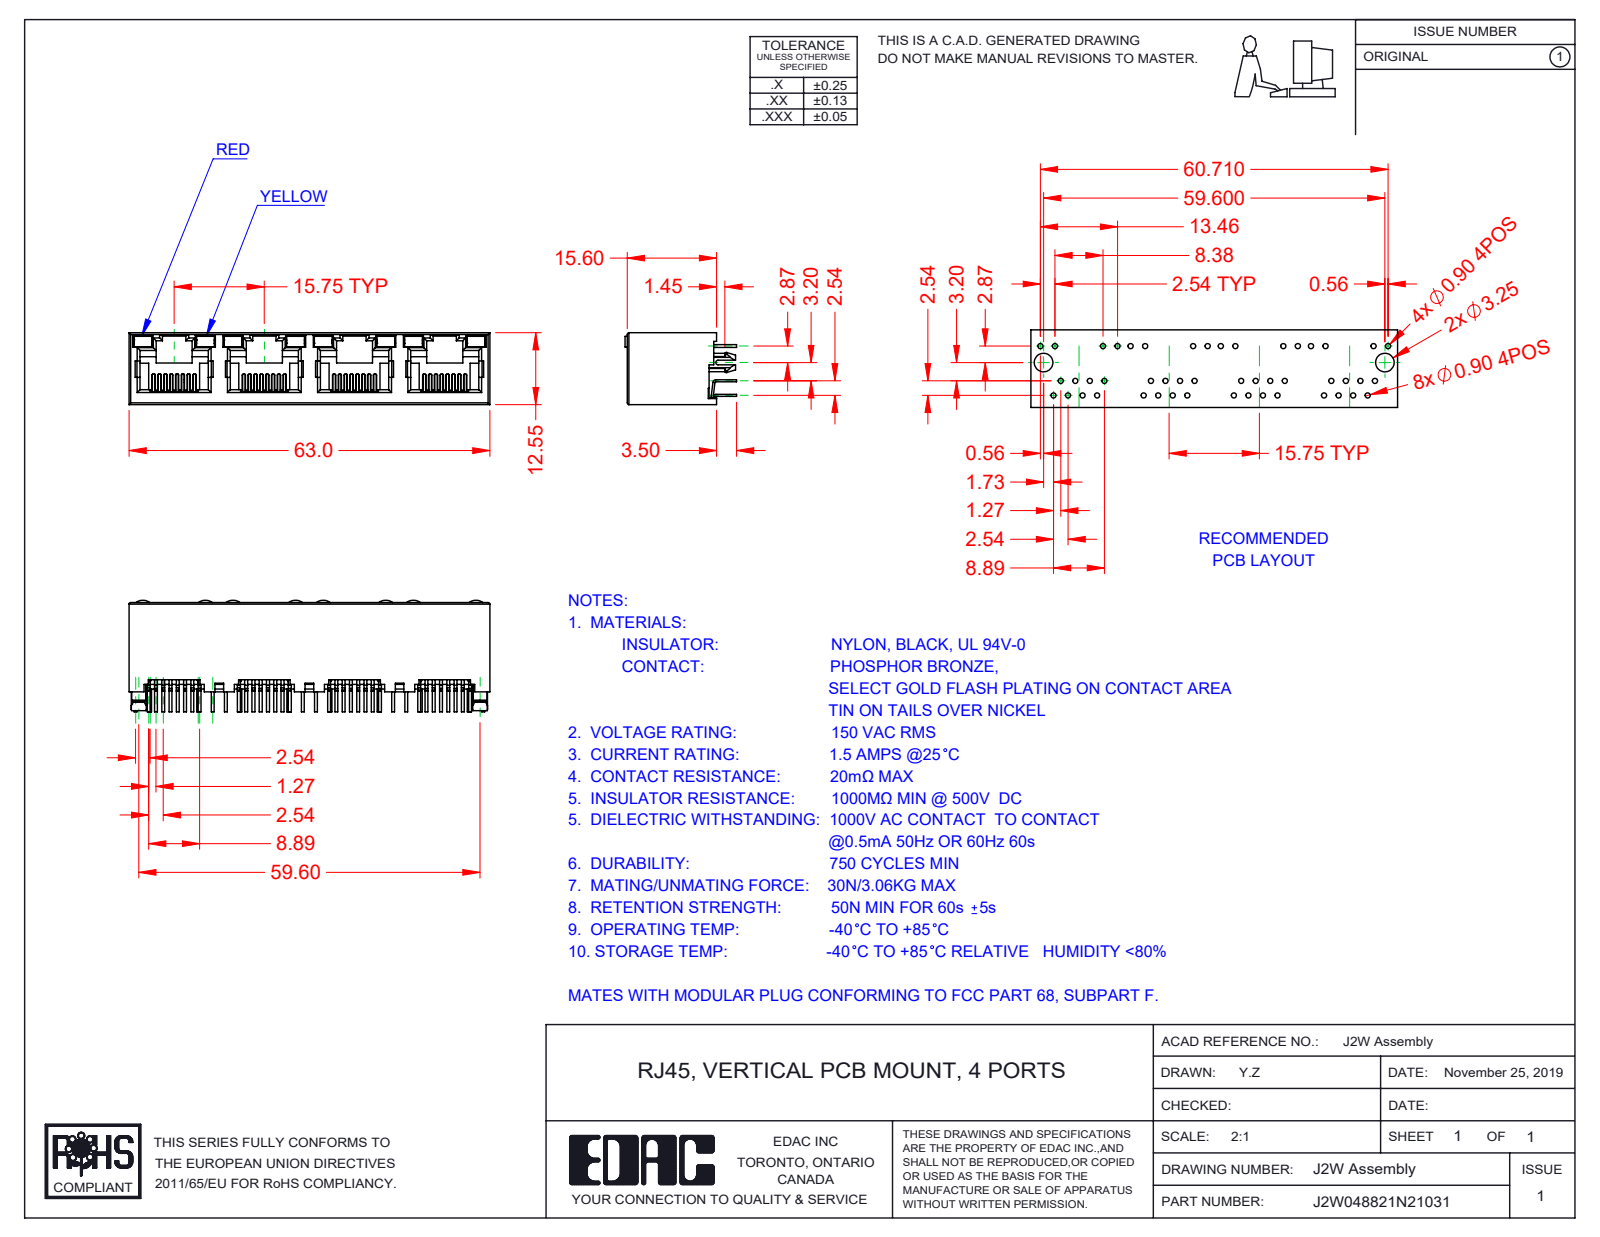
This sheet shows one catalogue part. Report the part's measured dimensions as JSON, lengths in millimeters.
{"part_name": "2W Contact Lock; 2W Contacts; 2W Insulator; 2W LED RH_1-Yellow (+2 more)", "step_written_by": "SolidWorks 2016 (CONFIG_CONTROL_DESIGN)", "units": "millimeters", "bodies": {"solids": 45, "faces": 3135, "planar": 2600, "cylindrical": 477, "other": 58}, "overall_size": [63, 19.5, 12.55], "volume_mm3": 5335, "surface_area_mm2": 13144, "partial_cylinders_radius": [[0.15, 64], [0.2, 29], [0.5, 28], [0.3, 14], [0.45, 8], [2, 8], [0.25, 2], [1.5, 2]], "face_to_face_distances": [12.55, 11.9, 0.65, 15.75, 0.36, 1.5, 0.78, 0.6, 11.3, 31.5]}
